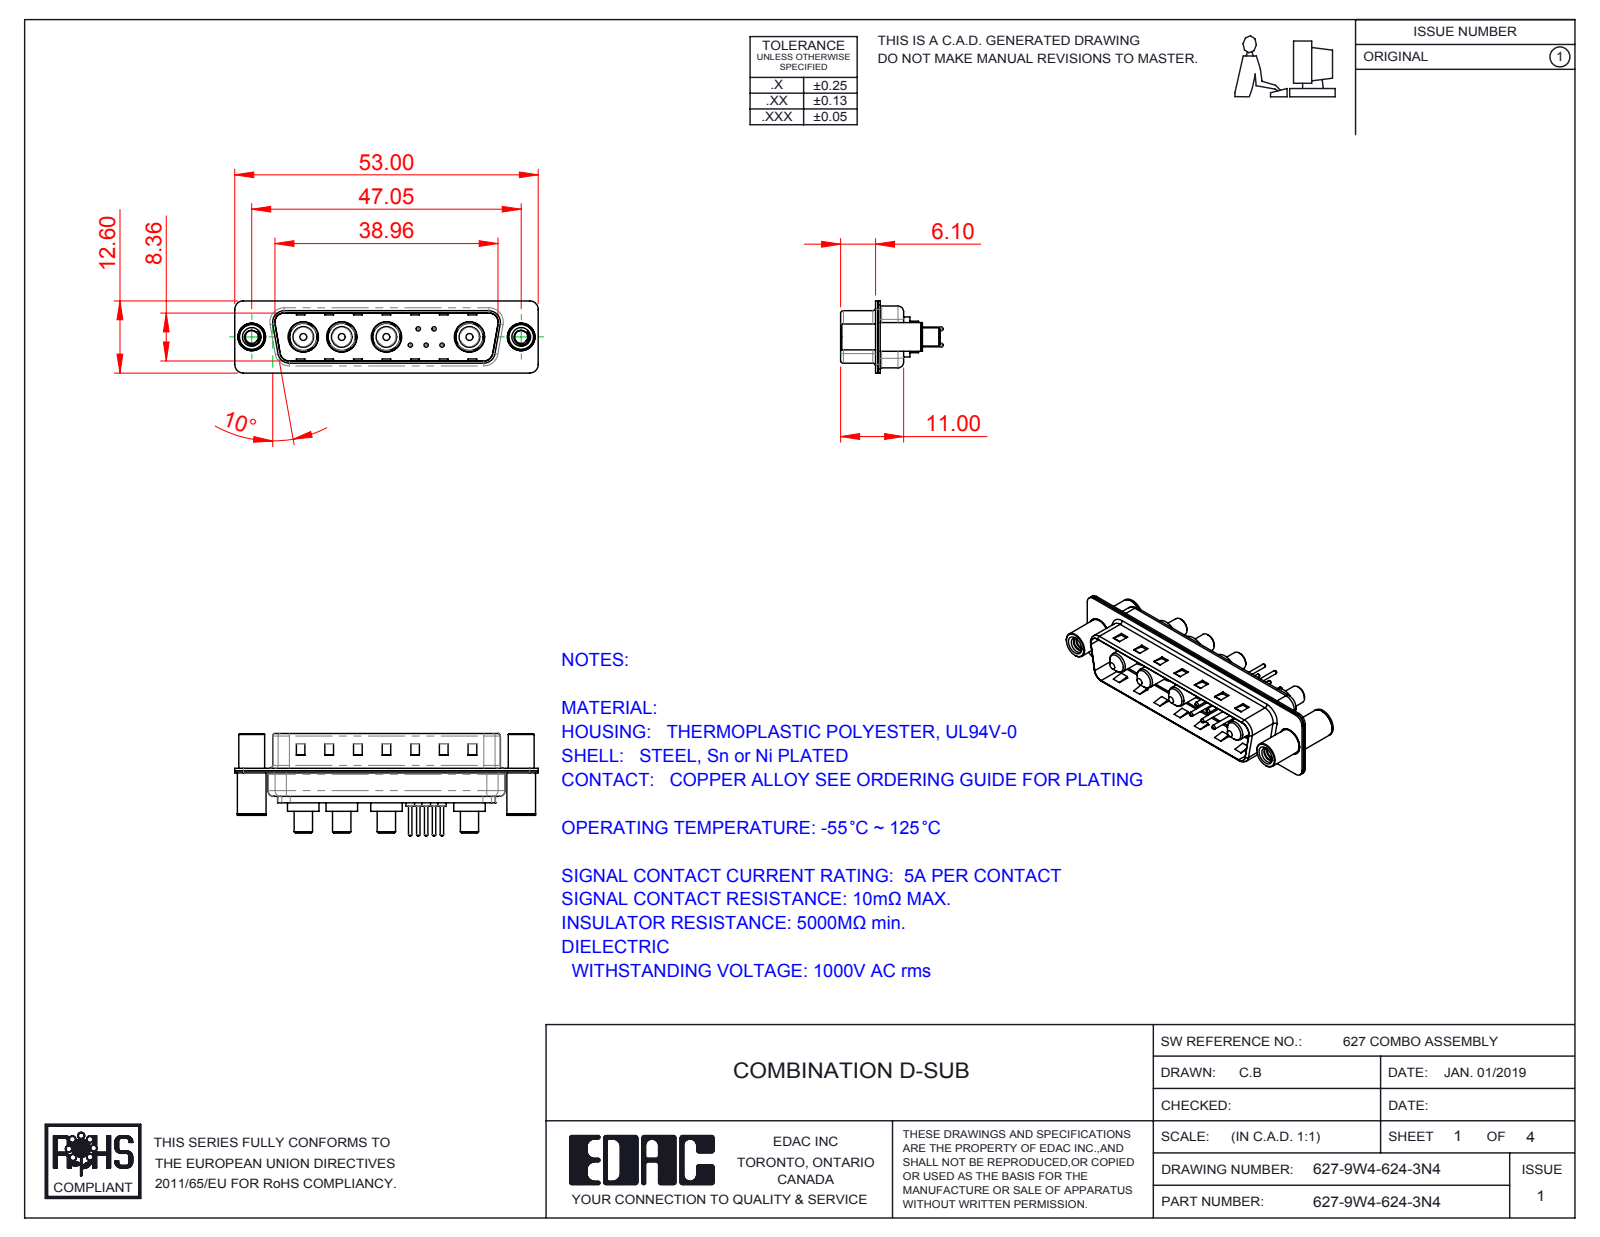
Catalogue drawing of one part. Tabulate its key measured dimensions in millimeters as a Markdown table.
| quantity | value |
| --- | --- |
| part name | Power Pin_30A S; 627-9W4-624-3N4; 627Combo Contact Row 2_24; 627Combo Contact Row 1_24 (+4 more) |
| STEP written by | SolidWorks 2016 (CONFIG_CONTROL_DESIGN) |
| units | millimeters |
| bodies | 18 solids, 807 faces (252 planar, 335 cylindrical, 220 other) |
| overall size | 53 × 17.9 × 12.6 |
| volume | 3 309 mm³ |
| surface area | 7 257 mm² |
| round holes (diameter × count) | 0.75 × 5, 1.6 × 5, 2 × 5, 4.85 × 4, 5.3 × 4, 2.26 × 2, 3.26 × 2, 4 × 2, 4.8 × 2 |
| round bosses / shafts (diameter × count) | 1.5 × 5, 0.6 × 5, 5.5 × 4, 5.2 × 4, 4.75 × 4, 3.75 × 4, 3.6 × 4, 3.2 × 4 |
| partial cylindrical surfaces (radius × count) | 1.5 × 16, 2 × 12, 0.5 × 8, 1.6 × 8, 0.25 × 4, 0.6 × 4, 0.65 × 4, 0.9 × 4 |
| main face-to-face distances | 0.4, 0.82, 9.58, 8.76, 1.5, 0.8, 5.6, 5.2, 6, 1.22 |
| hole center spacings | 3.16, 2.77, 5.04, 14.51, 2.78, 4.4, 4.41, 5 |
